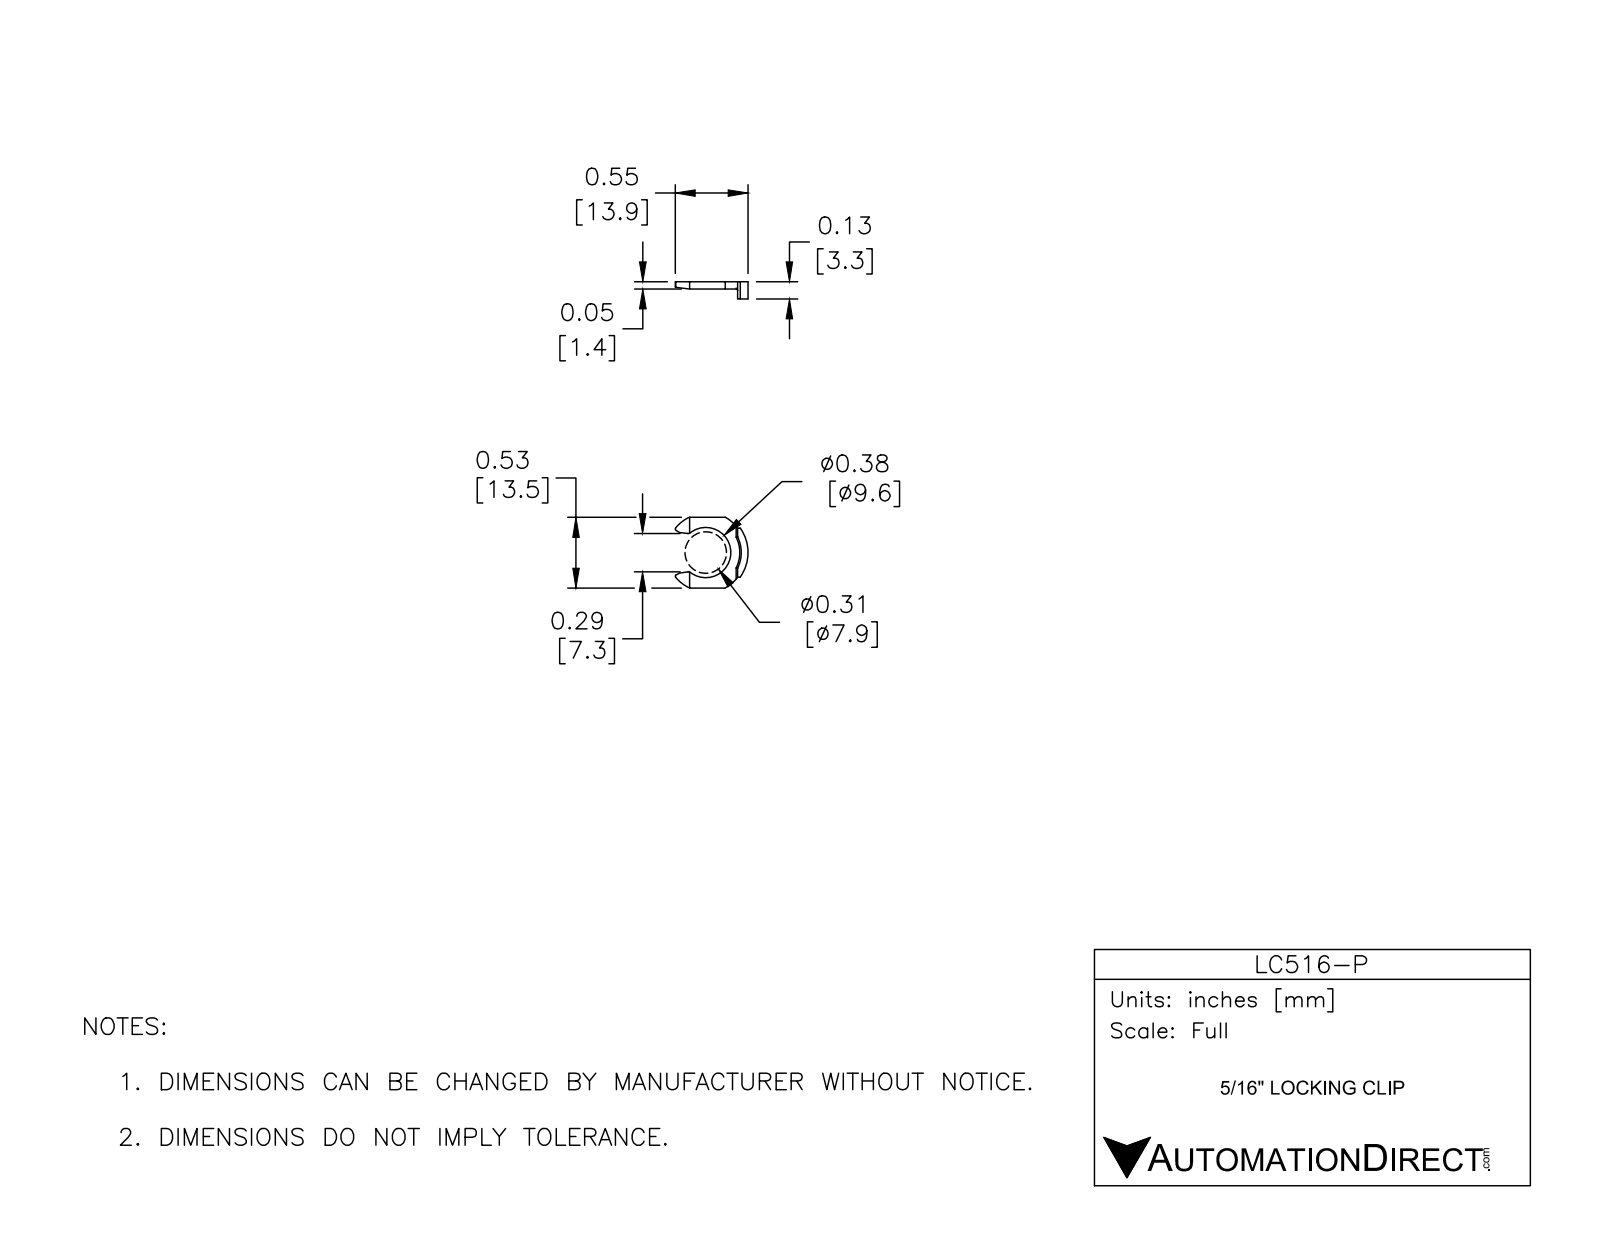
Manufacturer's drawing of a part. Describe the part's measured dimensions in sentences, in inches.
The part is named "LC516-P". Its 3-D file was written by "SolidWorks 2017 (AUTOMOTIVE_DESIGN)". It is 1 solid with 32 faces: 15 planar, 16 cylindrical and 1 other. Overall it measures 0.548 by 0.531 by 0.128 inches. Its volume is 0.008 cubic inches and its surface area 0.446 square inches. Partial cylindrical surfaces (rounded edges, fillets, slot ends): 3 of radius 0.012, 2 of radius 0.02, 1 of radius 0.189, 1 of radius 0.268, 1 of radius 0.292, 1 of radius 0.303, 1 of radius 0.319. The main face-to-face distances are 0.053, 0.128, 0.075, 0.531, 0.081, 0.451, 0.37.
